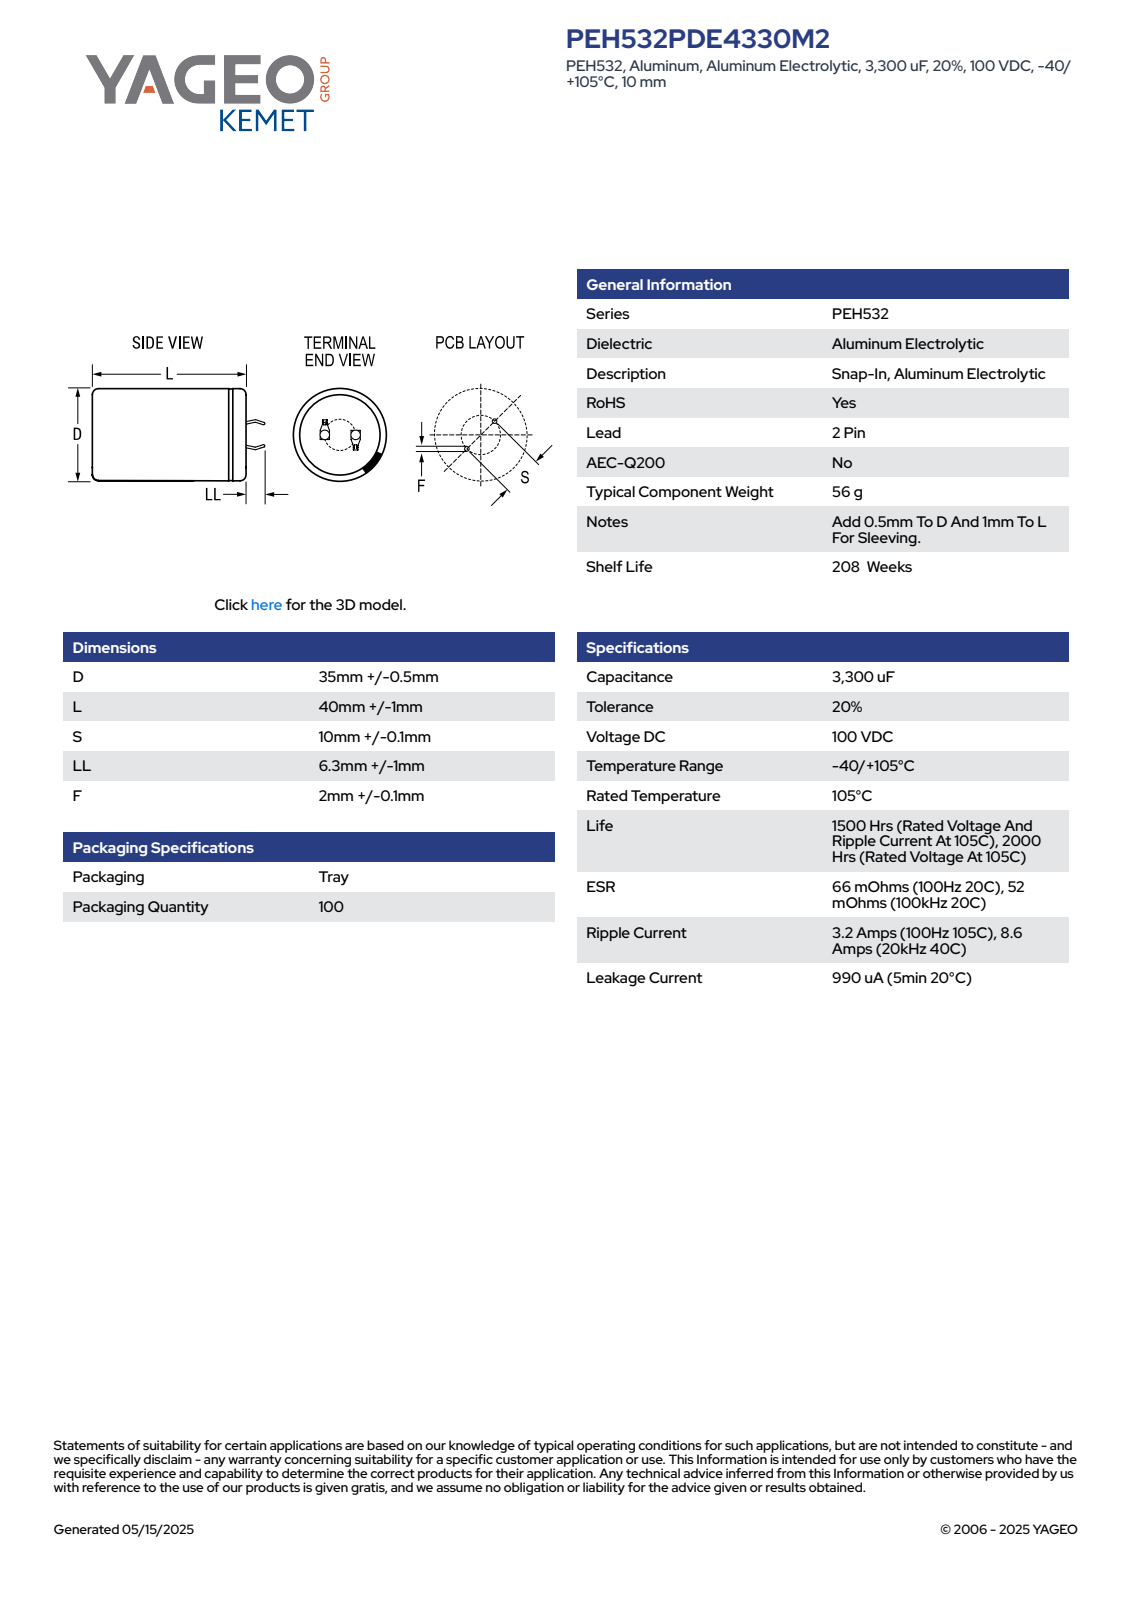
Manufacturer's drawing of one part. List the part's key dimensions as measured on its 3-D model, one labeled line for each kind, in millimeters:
Part name (STEP PRODUCT): CARS_K2P_35X40_D35.5L41S10LL7.3F2.1
STEP written by: SolidWorks 2014 (AUTOMOTIVE_DESIGN)
Units: millimetres
Bodies: 1 solid, 100 faces (52 planar, 9 cylindrical, 39 other)
Overall size (bounding box): 48.29 × 35.5 × 35.5
Volume: 40 076 mm³ · Surface area: 6 551 mm²
Round holes (diameter × count): ⌀31.41 ×1
Round bosses / shafts (diameter × count): ⌀35.5 ×1
Partial cylindrical surfaces — rounded edges, fillets, slot ends (radius × count): R17.74 ×1
Main face-to-face distances: 40.99, 0.6, 41.49, 0.5, 7.08, 7.64, 0.75, 1.35, 7.68, 6.48
